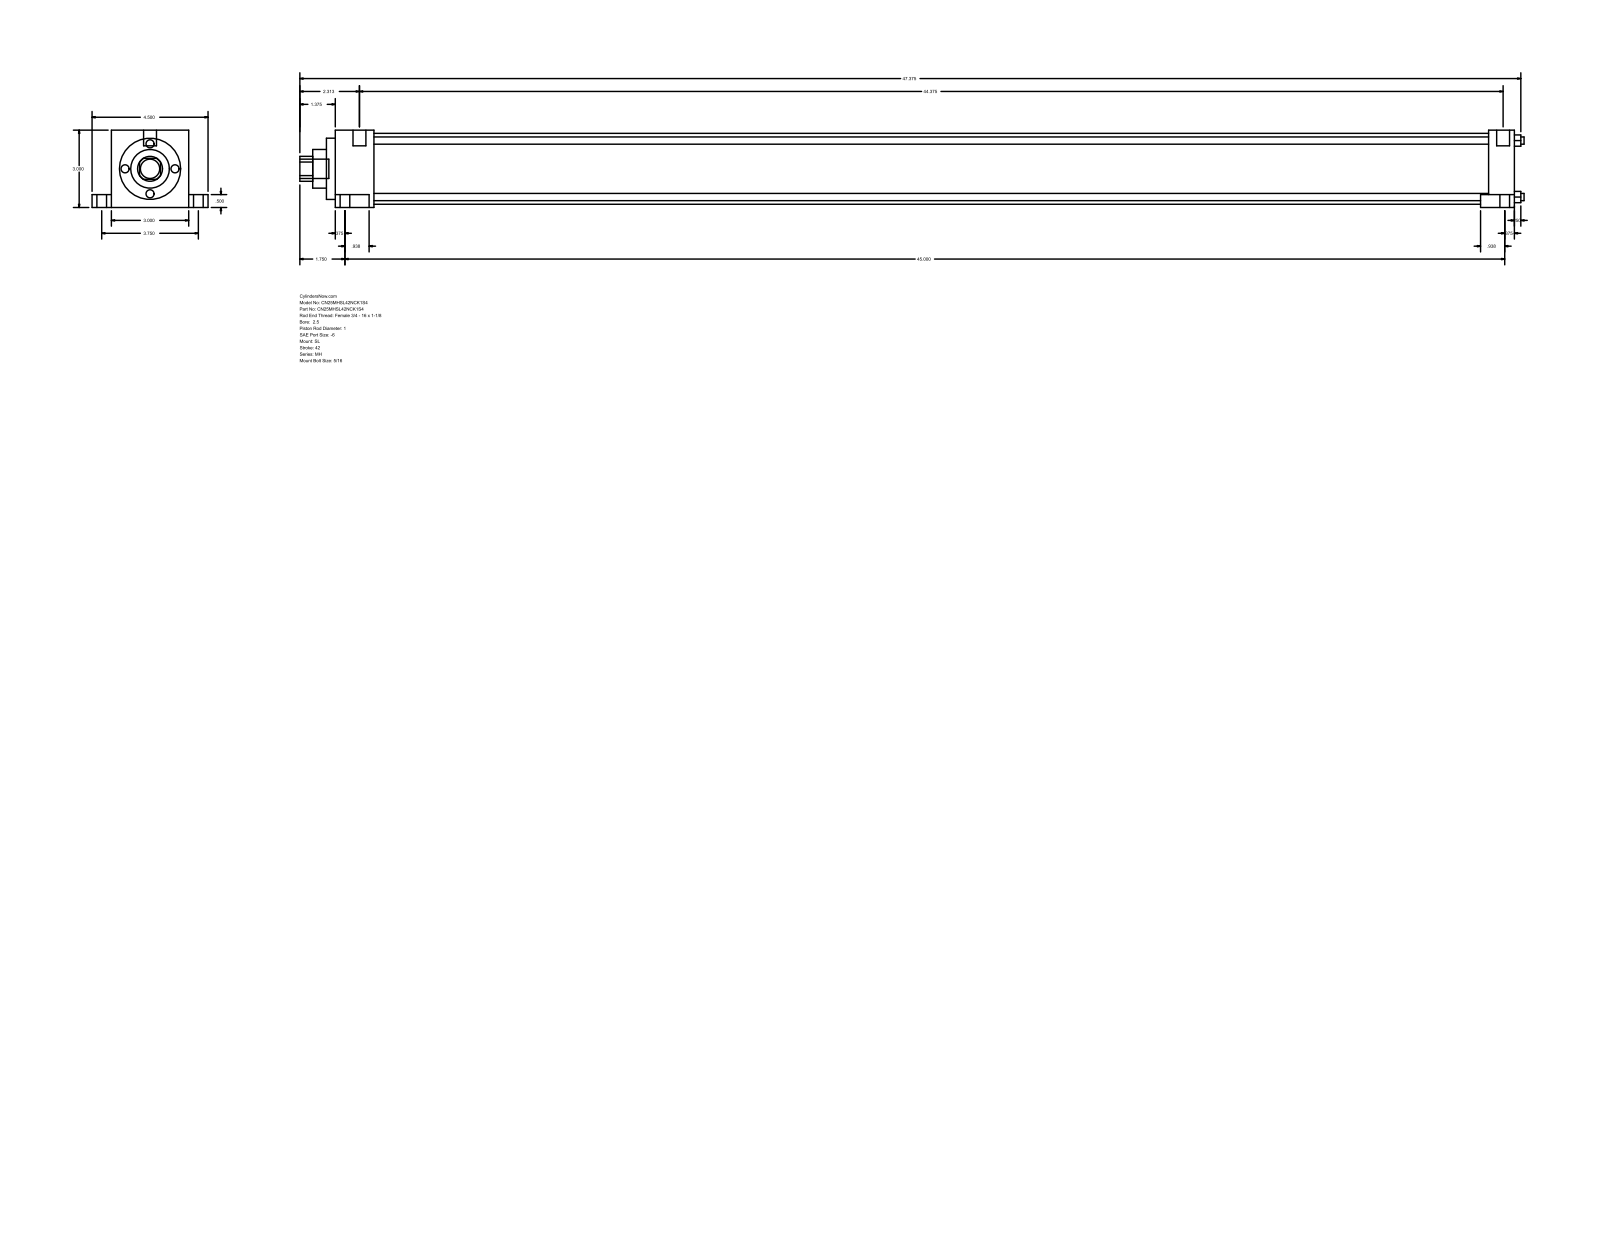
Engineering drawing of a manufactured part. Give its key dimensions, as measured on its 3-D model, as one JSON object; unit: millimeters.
{"part_name": "MH_SL__0250_1", "step_written_by": "GSSL Pune (CONFIG_CONTROL_DESIGN)", "units": "millimeters", "bodies": {"solids": 0, "faces": 86, "planar": 61, "cylindrical": 25, "other": 0}, "overall_size": [1206.5, 114.3, 76.2], "round_holes": [[7.14, 4], [25.4, 1], [38.1, 1], [60.33, 1], [69.85, 1]], "round_bosses_or_shafts": [[15.88, 2], [9.53, 2], [5.56, 2], [19.05, 1], [12.7, 1]], "partial_cylinders_radius": [[12.29, 1]], "face_to_face_distances": [76.2, 25.39, 1145.39, 1170.78, 12.7, 63.5, 19.05, 95.25, 13.49, 1158.88], "hole_center_spacings": [39.33, 55.62, 78.66]}
